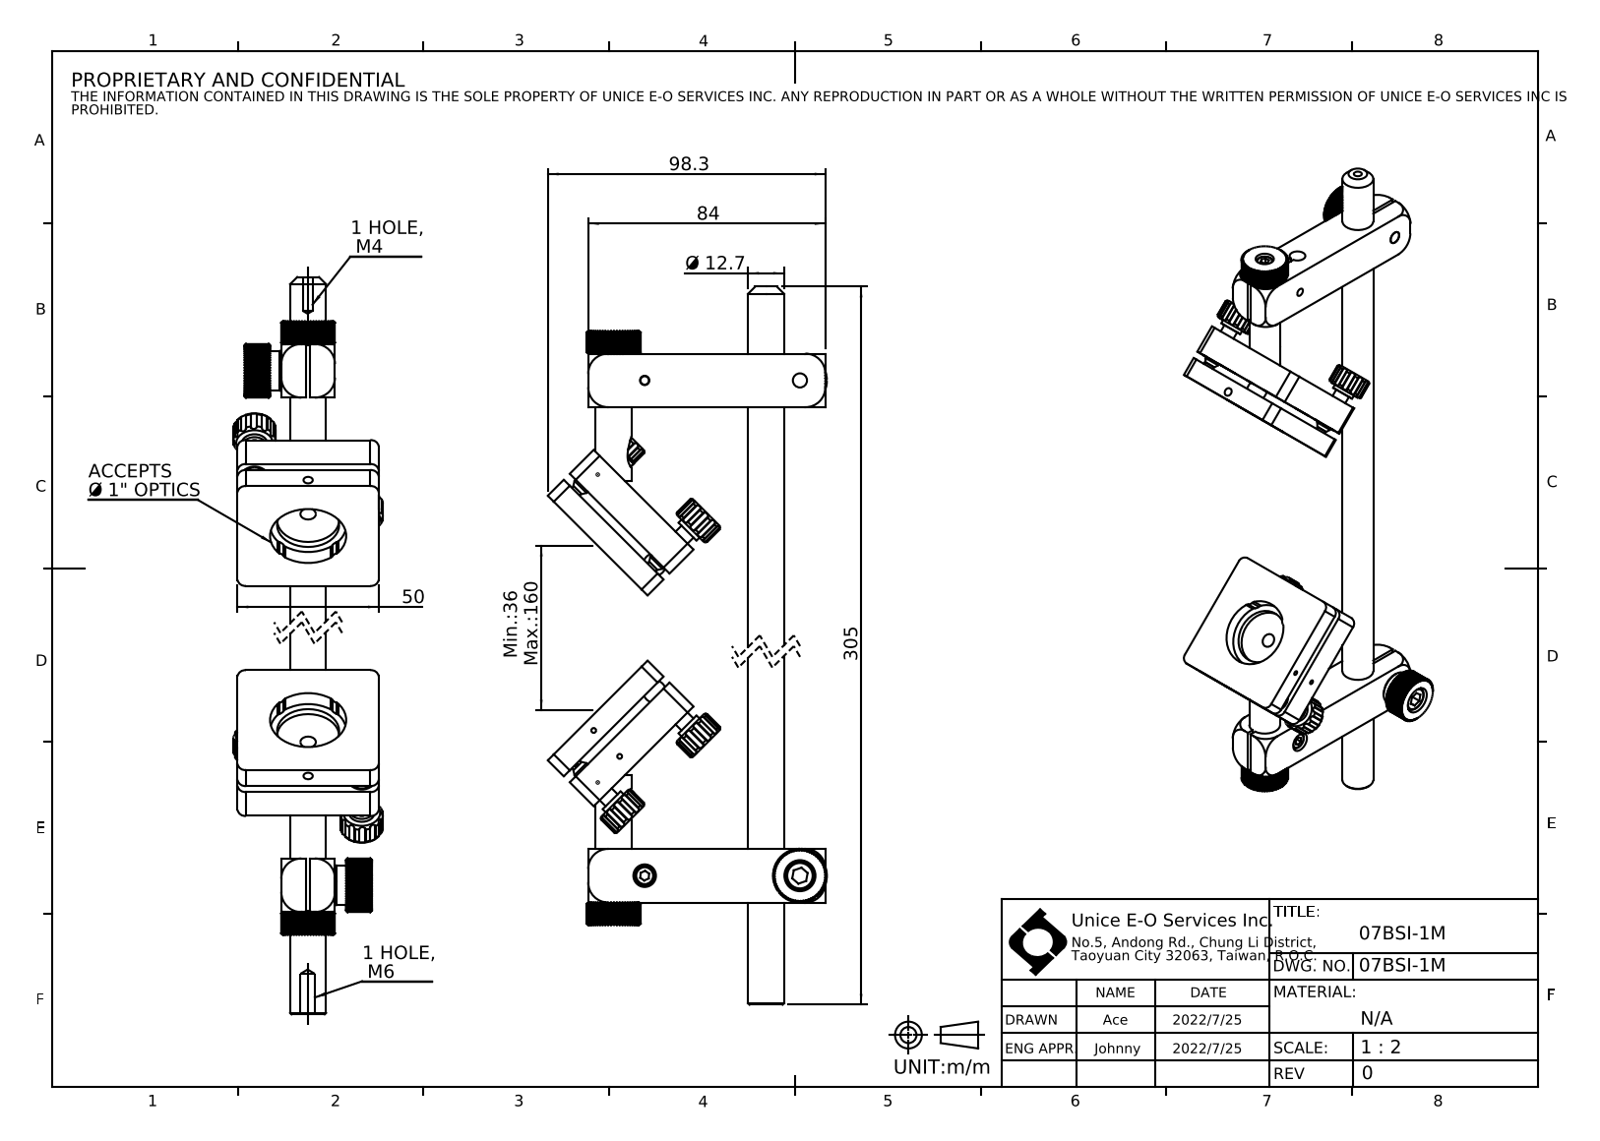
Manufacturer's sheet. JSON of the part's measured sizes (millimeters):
{"part_name": "07BSI-1M", "step_written_by": "SolidWorks 2021 (CONFIG_CONTROL_DESIGN)", "units": "millimeters", "bodies": {"solids": 46, "faces": 2164, "planar": 742, "cylindrical": 770, "other": 652}, "overall_size": [305, 98.82, 52.96], "volume_mm3": 200561, "surface_area_mm2": 86569, "round_holes": [[1.7, 8], [3.3, 8], [7, 7], [4, 4], [4.5, 4], [4.7, 4], [5.19, 4], [5.75, 4], [6.3, 4], [8, 4], [9.5, 4], [5, 3]], "round_bosses_or_shafts": [[6, 6], [7, 5], [4, 5], [9.45, 4], [9, 4], [1.5, 4], [14, 2], [10, 2]], "partial_cylinders_radius": [[0.3, 96], [1.5, 50], [3, 14], [0.75, 8], [2, 8], [2.5, 4], [7.5, 4], [9.5, 3]], "face_to_face_distances": [19, 8, 3, 11, 15.5, 34.5, 226.05, 12, 11.99, 14.99], "hole_center_spacings": [13, 26.87, 19.92, 45.49, 19.93, 100.9, 15, 19.42]}
